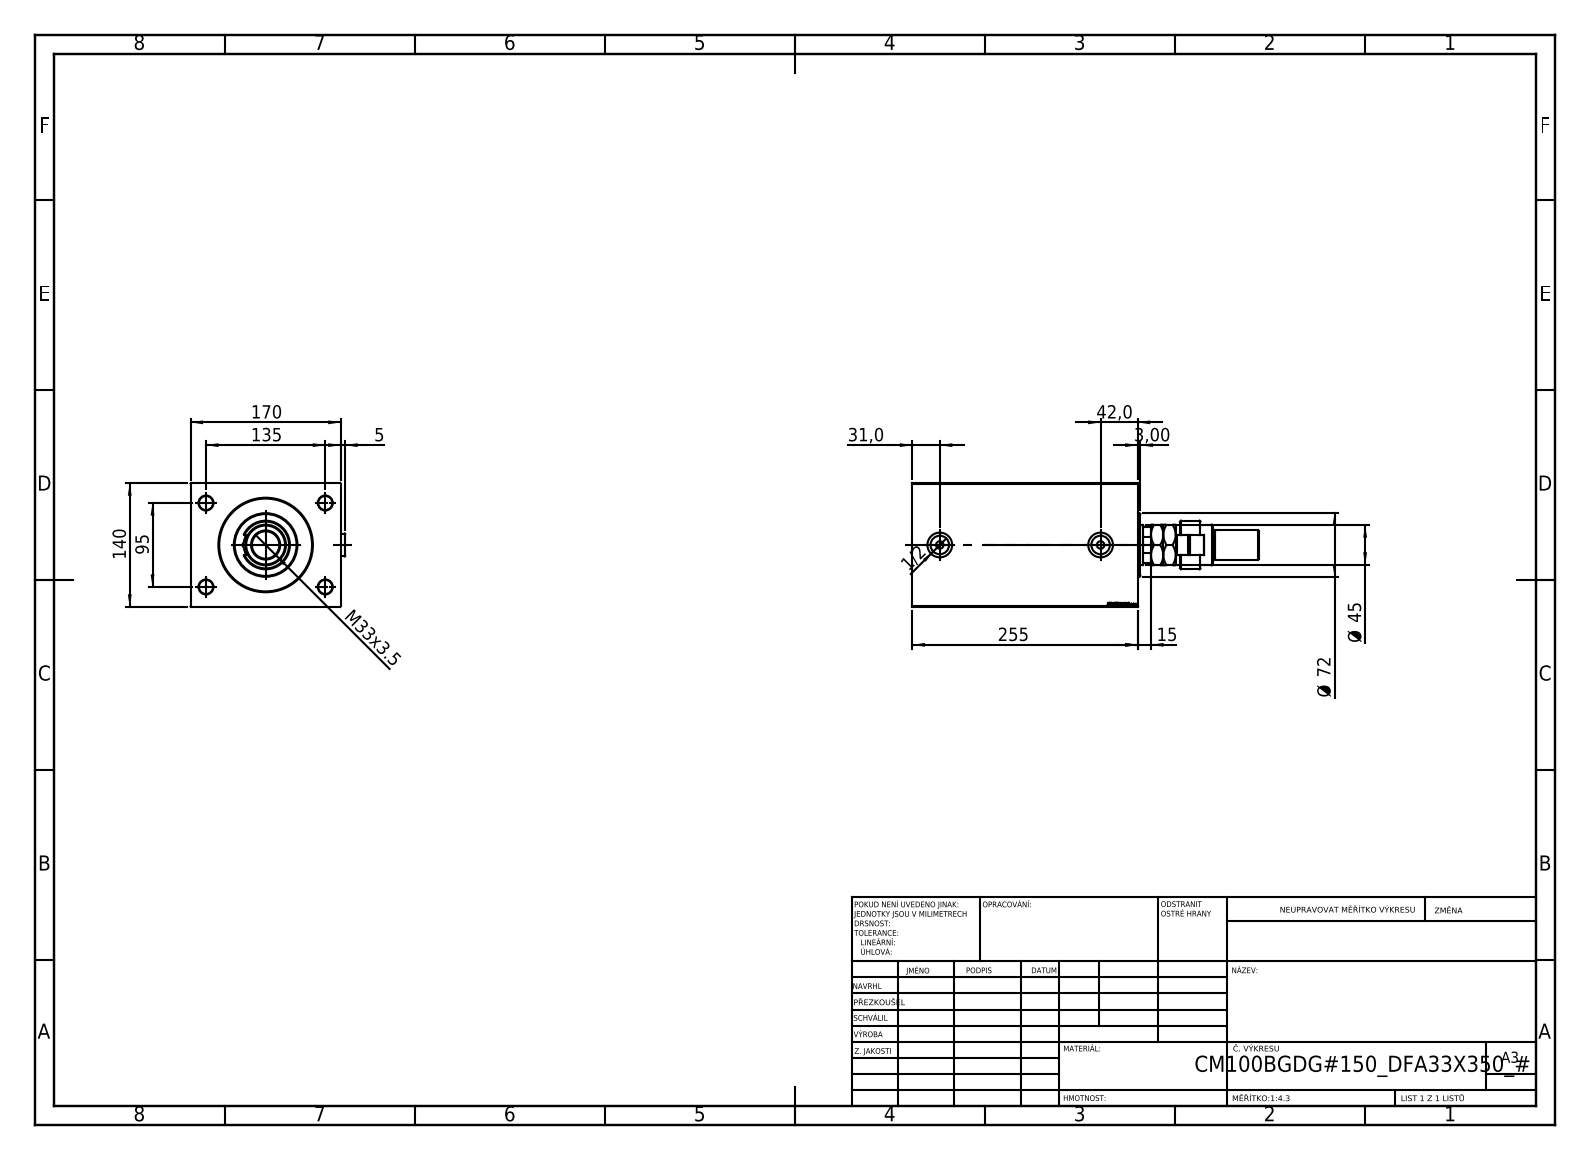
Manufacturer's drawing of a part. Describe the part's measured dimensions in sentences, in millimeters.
The part is named "Zatka_OIL_PORT; MFA; V450CM_B_VCP; V450CM_VC_B (+2 more)". Its 3-D file was written by "SolidWorks 2019 (CONFIG_CONTROL_DESIGN)". It is 6 solids with 1023 faces: 464 planar, 85 cylindrical and 474 other. Overall it measures 392 by 174.9 by 140 millimeters. Its volume is 1 031 000 cubic millimeters and its surface area 415 956 square millimeters. Round holes: 4 of diameter 16, 2 of diameter 8.5, 2 of diameter 20.96, 2 of diameter 28, 1 of diameter 31.5, 1 of diameter 39, 1 of diameter 45, 1 of diameter 48.5, 1 of diameter 49.5, 1 of diameter 100, 1 of diameter 102, 1 of diameter 105. Round bosses or shafts: 2 of diameter 26, 1 of diameter 72, 1 of diameter 55, 1 of diameter 46, 1 of diameter 35, 1 of diameter 33, 1 of diameter 31, 1 of diameter 22. Partial cylindrical surfaces (rounded edges, fillets, slot ends): 1 of radius 11.5, 1 of radius 22. The main face-to-face distances are 140, 170, 255, 26, 229, 15, 90, 240, 64, 214. The hole center spacings are 82.54, 95, 135, 165.08, 182.
